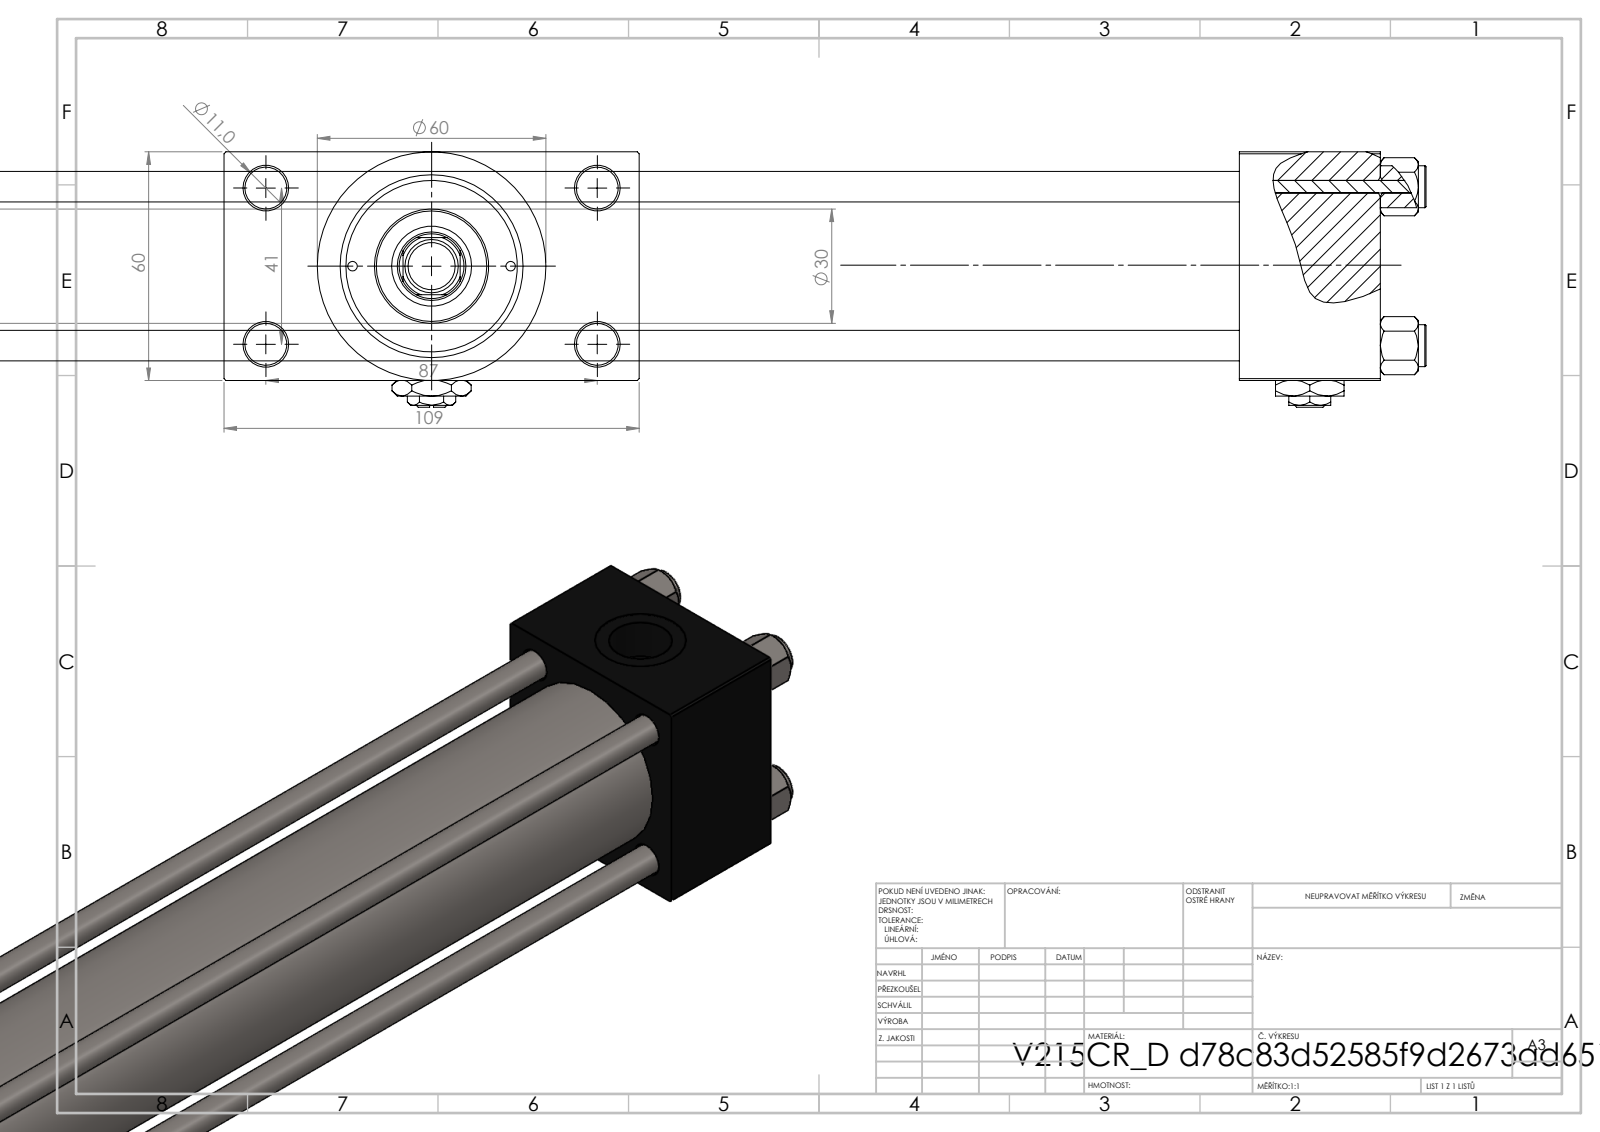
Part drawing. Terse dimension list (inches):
name: Zatka_pro_OIL_PORT; V215CR_D_Body; V215_VC_A; NUT_M5_D (+3 more)
written by: SolidWorks 2019 (CONFIG_CONTROL_DESIGN)
unit: in
bodies: 14 solids, 1228 faces (552 planar, 108 cylindrical, 568 other)
size: 19.016 × 4.291 × 2.638
volume: 46.32 in³; area: 379.2 in²
holes: 4× ⌀0.315, 4× ⌀0.433, 2× ⌀0.098, 2× ⌀0.276, 2× ⌀0.656, 2× ⌀0.945, 1× ⌀0.335, 1× ⌀0.709, 1× ⌀0.827, 1× ⌀1.22, 1× ⌀1.575, 1× ⌀1.772
bosses: 4× ⌀0.433, 1× ⌀2.362, 1× ⌀1.811, 1× ⌀1.181, 1× ⌀0.551, 1× ⌀0.472
rounds: 1× R0.335
face distances: 2.362, 0.965, 3.327, 13.307, 1.457, 14.764, 1.693, 16.457, 15, 4.291
hole spacings: 0.821, 0.892, 1.161, 1.206, 1.642, 1.832, 1.856, 1.893
